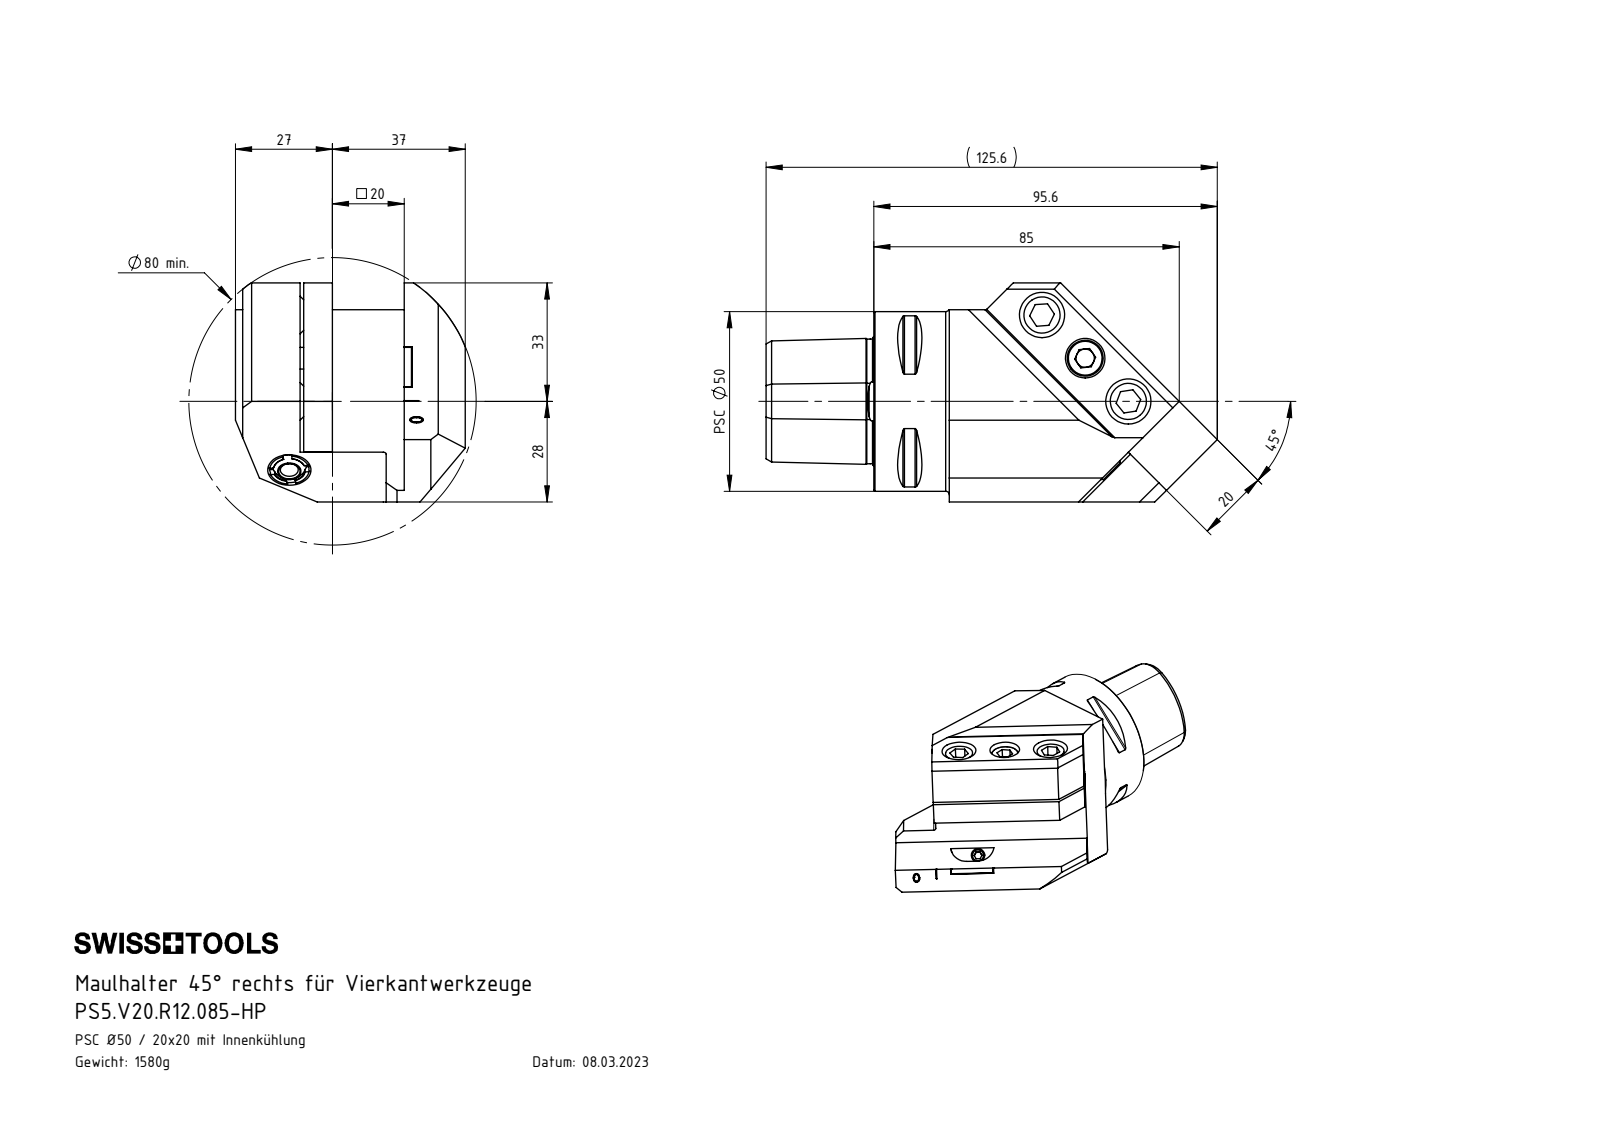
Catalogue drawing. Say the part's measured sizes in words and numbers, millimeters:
The part is named "PS5-V20.R12.085-HP_A_ohne platte; DIN 3771 - 8x1.5; KU1-U12.002.010_A; KU1-U12.003.010_B (+8 more)". Its 3-D file was written by "SolidWorks 2017 (AUTOMOTIVE_DESIGN)". It is 13 solids with 396 faces: 135 planar, 83 cylindrical and 178 other. Overall it measures 125.61 by 64 by 61 millimeters. Its volume is 201 327 cubic millimeters and its surface area 39 161 square millimeters. Round holes: 4 of diameter 5, 2 of diameter 4.2, 2 of diameter 10, 2 of diameter 10.2, 2 of diameter 11, 1 of diameter 4, 1 of diameter 6.1, 1 of diameter 6.8, 1 of diameter 8.5, 1 of diameter 14.5, 1 of diameter 16.3, 1 of diameter 21. Round bosses or shafts: 3 of diameter 12, 2 of diameter 5, 1 of diameter 50, 1 of diameter 10, 1 of diameter 6. Partial cylindrical surfaces (rounded edges, fillets, slot ends): 8 of radius 0.5, 2 of radius 0.8, 2 of radius 6, 1 of radius 4.4, 1 of radius 5, 1 of radius 40. The main face-to-face distances are 20, 17, 45, 8, 28, 37, 1, 9, 46, 29. The hole center spacings are 17, 26, 34, 42.31, 48.36, 58.86, 65.4, 73.83.
